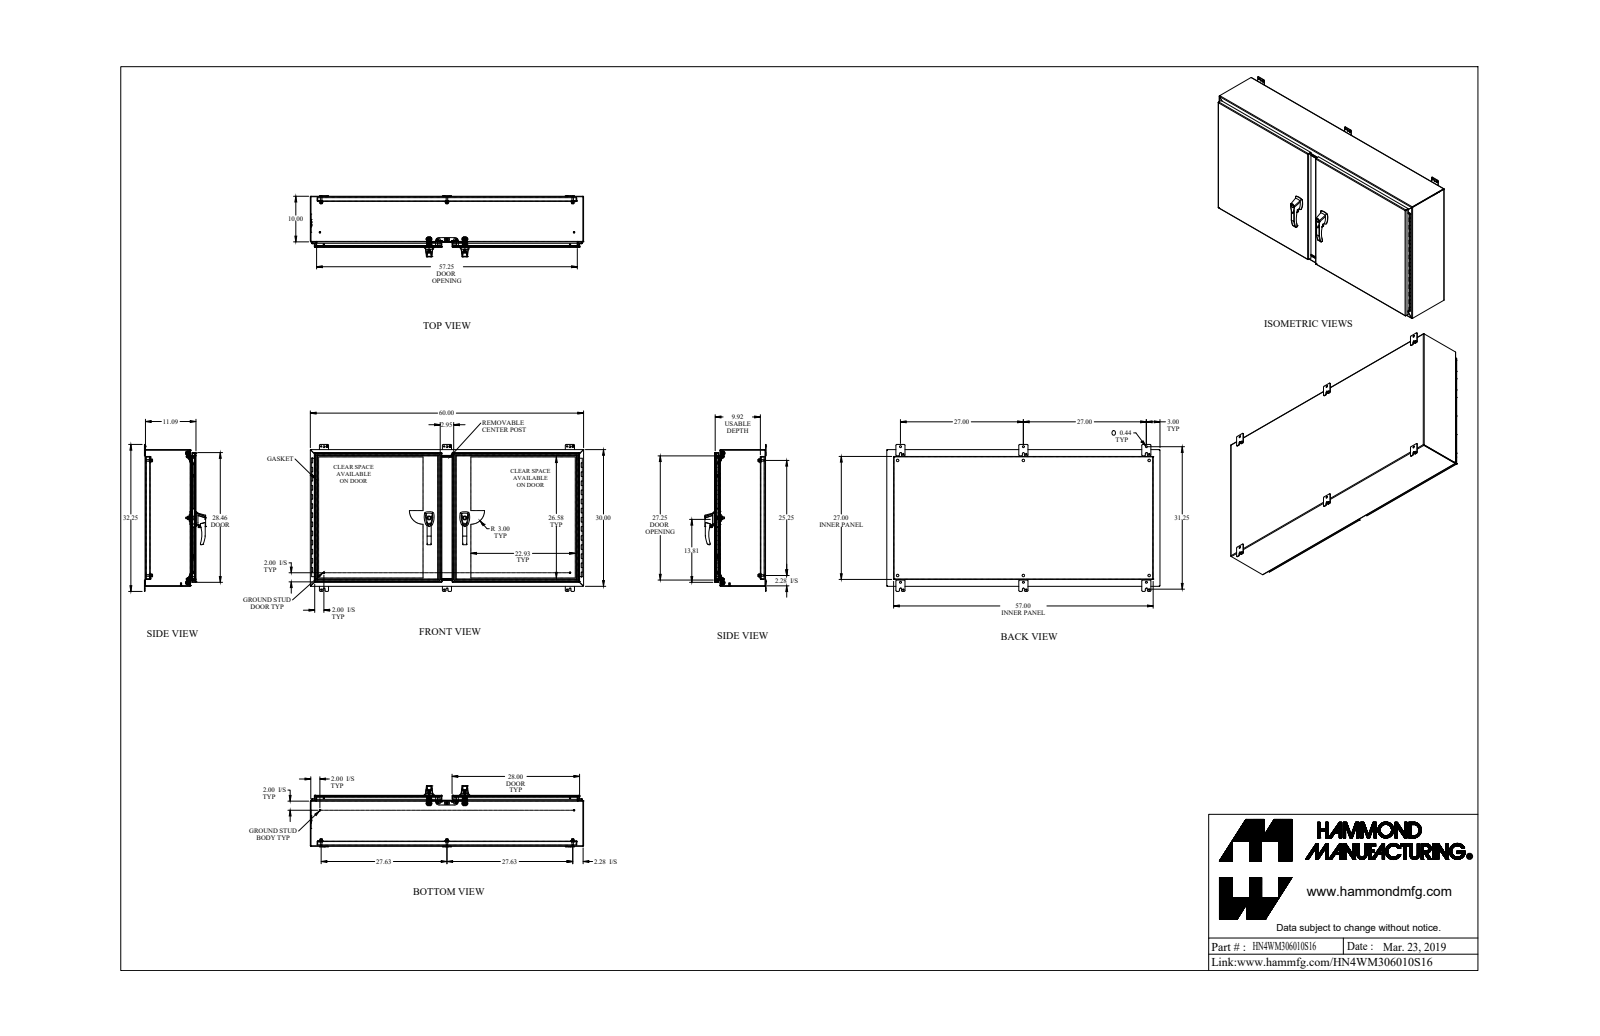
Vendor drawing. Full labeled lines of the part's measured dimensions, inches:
Part name (STEP PRODUCT): HN4WM306010S16
STEP written by: SolidWorks 2018 (AUTOMOTIVE_DESIGN)
Units: inches
Bodies: 103 solids, 2768 faces (1307 planar, 1179 cylindrical, 282 other)
Overall size (bounding box): 60 × 32.25 × 13.425
Volume: 799.9 in³ · Surface area: 16 597 in²
Round holes (diameter × count): ⌀0.304 ×10, ⌀0.313 ×6, ⌀0.563 ×6, ⌀0.25 ×5, ⌀0.307 ×5, ⌀0.281 ×4, ⌀0.313 ×4, ⌀0.39 ×4, ⌀0.445 ×4, ⌀0.201 ×3, ⌀0.437 ×3, ⌀0.11 ×2
Round bosses / shafts (diameter × count): ⌀1 ×7, ⌀0.65 ×5, ⌀0.375 ×5, ⌀0.332 ×5, ⌀0.75 ×4, ⌀0.625 ×4, ⌀0.44 ×4, ⌀0.37 ×4
Partial cylindrical surfaces — rounded edges, fillets, slot ends (radius × count): R0.125 ×33, R0.018 ×32, R0.188 ×27, R0.25 ×26, R0.048 ×23, R0.143 ×23, R0.06 ×20, R0.5 ×18
Main face-to-face distances: 0.095, 1.032, 11.09, 10.995, 0.095, 11.185, 11.09, 0.937, 1.127, 9.963
Hole centre spacings: 27.625, 37.426, 6, 58.429, 26.869, 33.965, 60.746, 12
